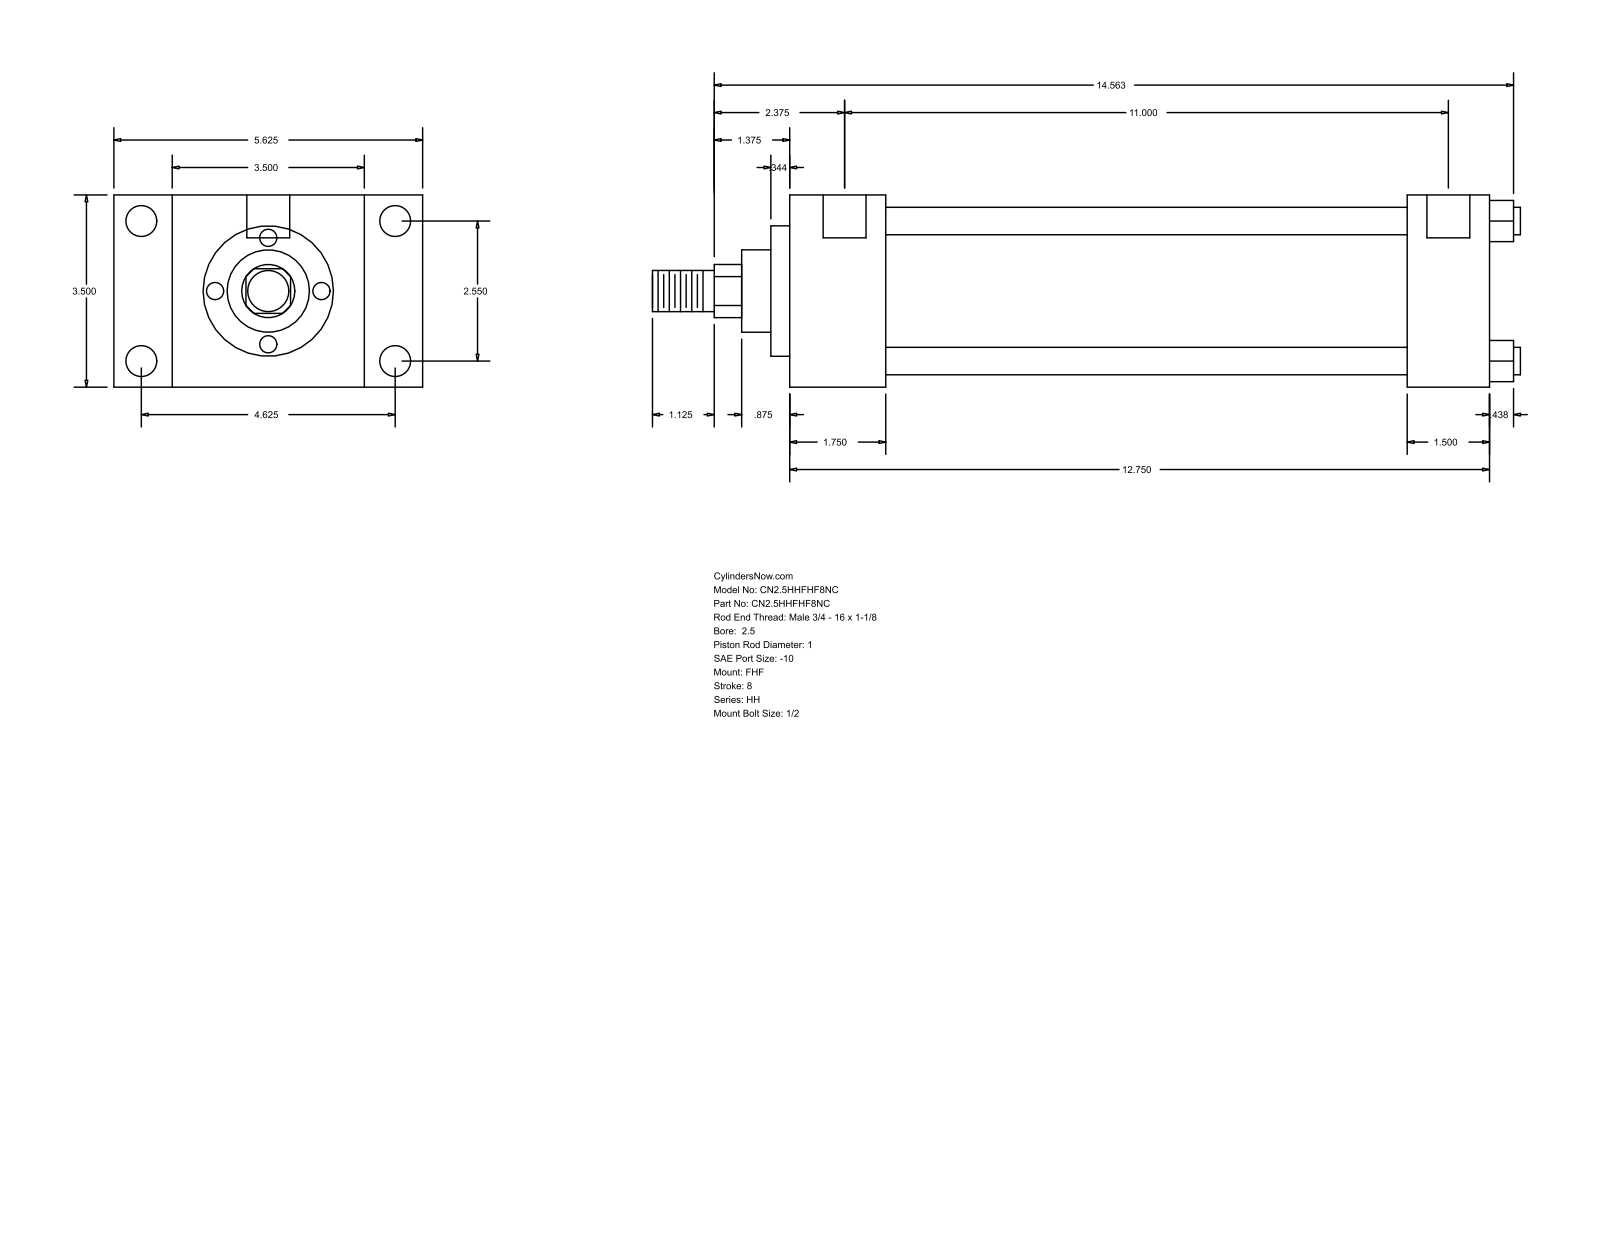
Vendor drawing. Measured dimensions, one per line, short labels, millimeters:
name: HH_FHF__0250_1
written by: GSSL Pune (CONFIG_CONTROL_DESIGN)
unit: mm
bodies: 0 solids, 90 faces (61 planar, 29 cylindrical, 0 other)
size: 401.64 × 142.88 × 88.9
holes: 4× ⌀5.56, 4× ⌀14.3, 2× ⌀19.84
bosses: 4× ⌀12.7, 1× ⌀73.03, 1× ⌀60.33, 1× ⌀38.1, 1× ⌀25.4, 1× ⌀19.05
rounds: 1× R12.29
face distances: 88.9, 44.46, 26.99, 115.89, 323.85, 279.39, 142.88, 285.76, 241.3, 38.09
hole spacings: 64.76, 117.48, 134.15, 282.57, 1.58, 1.59, 279.4, 280.98
